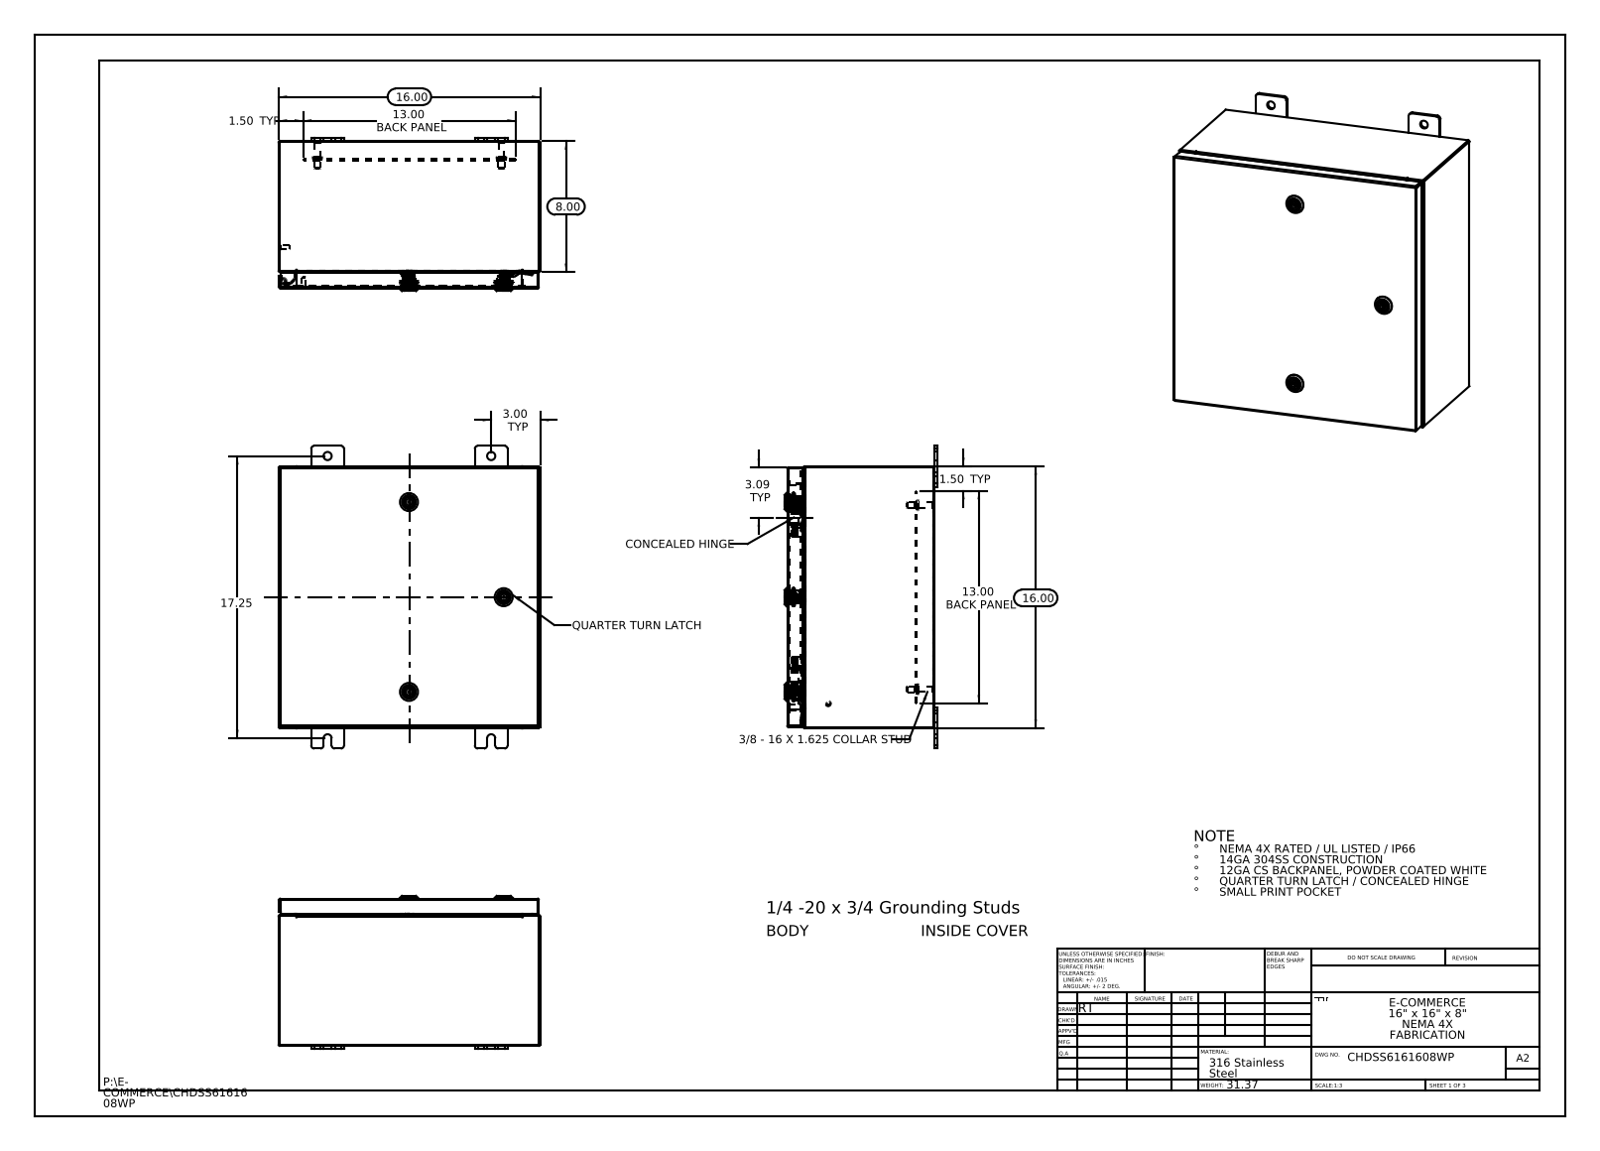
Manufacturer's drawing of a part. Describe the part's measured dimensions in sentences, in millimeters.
The part is named "CHDSS6161608WP Cover; Quarter-20 CD Stud; Housing-211301-IB-Industrilas_Housing-211301-IB-Industrilas; Insert-221320-IB-Industrilas_Insert-221320-IB-Industrilas (+8 more)". Its 3-D file was written by "SolidWorks 2013 (CONFIG_CONTROL_DESIGN)". It is 37 solids with 2966 faces: 938 planar, 930 cylindrical and 1098 other. Overall it measures 469.9 by 406.4 by 237.6 millimeters. Its volume is 1 837 000 cubic millimeters and its surface area 1 829 000 square millimeters. Round holes: 8 of diameter 12.7, 4 of diameter 3.5, 3 of diameter 5, 3 of diameter 10, 3 of diameter 10.2, 3 of diameter 16, 3 of diameter 20, 1 of diameter 5.4. Round bosses or shafts: 5 of diameter 6, 4 of diameter 15.9, 4 of diameter 9.5, 4 of diameter 8.4, 3 of diameter 28, 3 of diameter 19.8, 3 of diameter 15.9, 3 of diameter 15.5. Partial cylindrical surfaces (rounded edges, fillets, slot ends): 99 of radius 0.2, 99 of radius 3, 36 of radius 0.7, 24 of radius 4.8, 18 of radius 0.3, 18 of radius 2.2, 12 of radius 0.5, 12 of radius 5. The main face-to-face distances are 1.9, 404.5, 1.9, 402.6, 406.4, 228.9, 226.9, 227, 225.1, 25.4. The hole center spacings are 17.5, 47.2, 77.9, 142.9, 246, 254, 285.8, 285.8.
